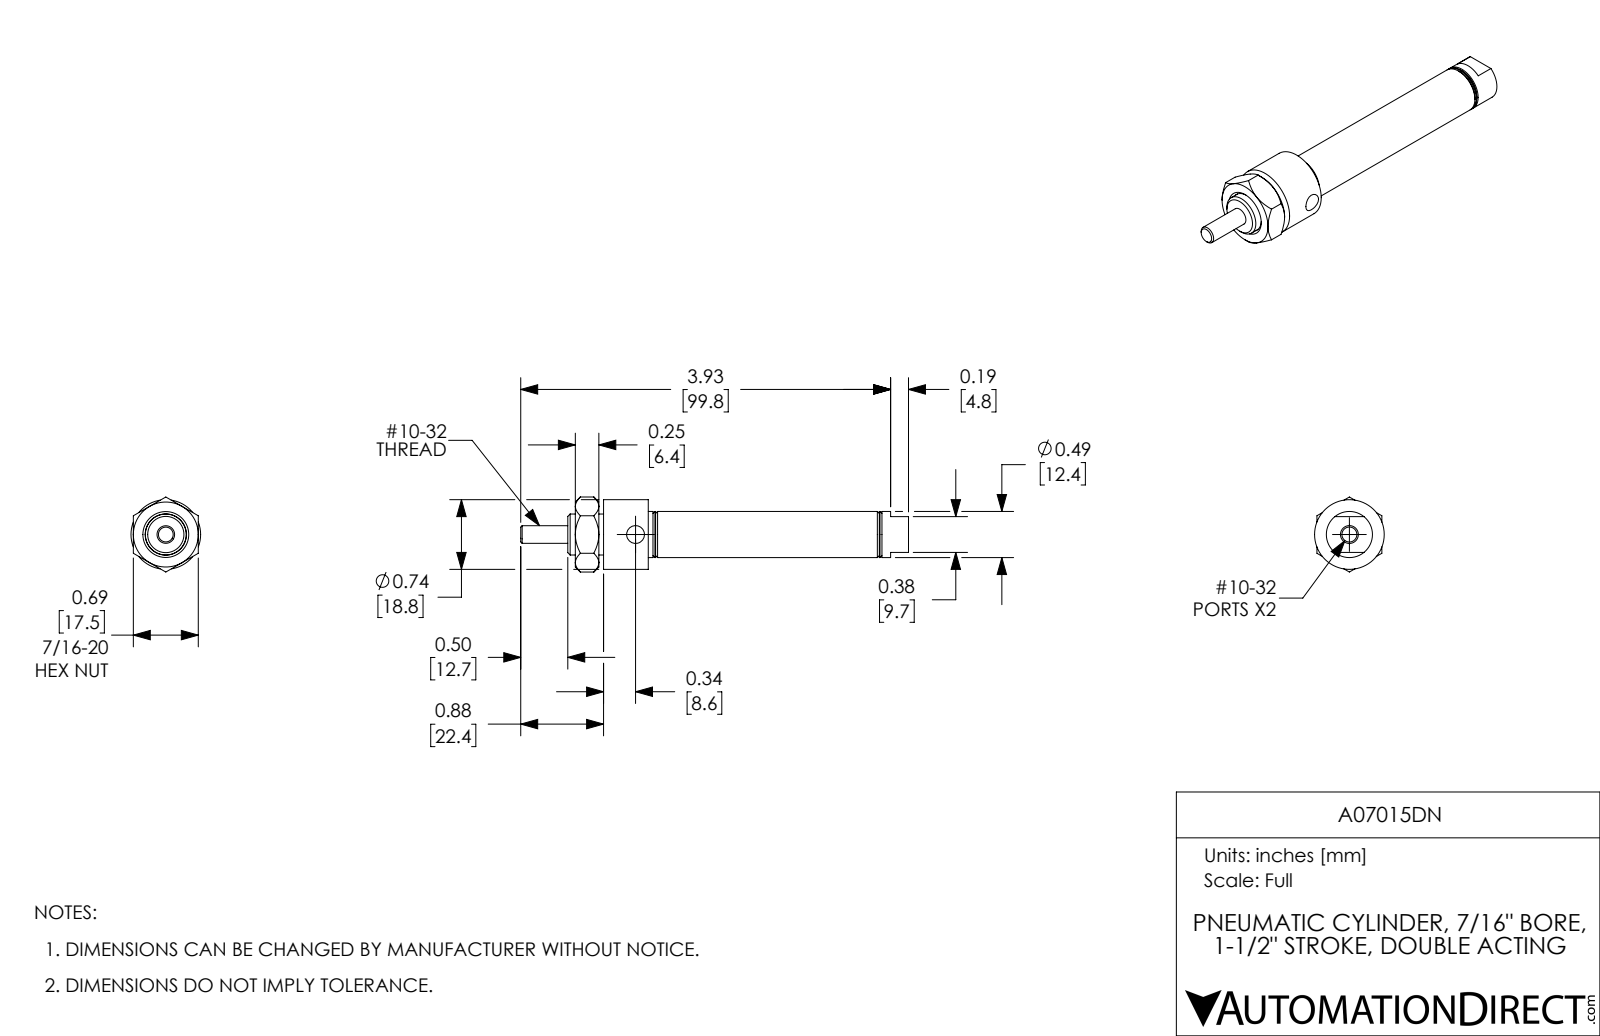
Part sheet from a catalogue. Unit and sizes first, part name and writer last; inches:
Units: inches
Overall size (bounding box): 4.12 × 0.797 × 0.74
Round holes (diameter × count): ⌀0.159 ×2, ⌀0.19 ×2, ⌀0.187 ×1, ⌀0.437 ×1
Round bosses / shafts (diameter × count): ⌀0.74 ×1, ⌀0.49 ×1, ⌀0.435 ×1
Main face-to-face distances: 2.62, 0.62, 0.69, 2.145, 0.475, 0.05, 0.525, 2.92, 0.775, 0.3
Volume: 0.644 in³ · Surface area: 15.05 in²
Bodies: 3 solids, 92 faces (28 planar, 32 cylindrical, 32 other)
Part name (STEP PRODUCT): A07015DN-Rod; A07015DN_Mounting Nut_D-154; A07015DN-MainBody; A07015DN
STEP written by: SolidWorks 2017 (AUTOMOTIVE_DESIGN)
